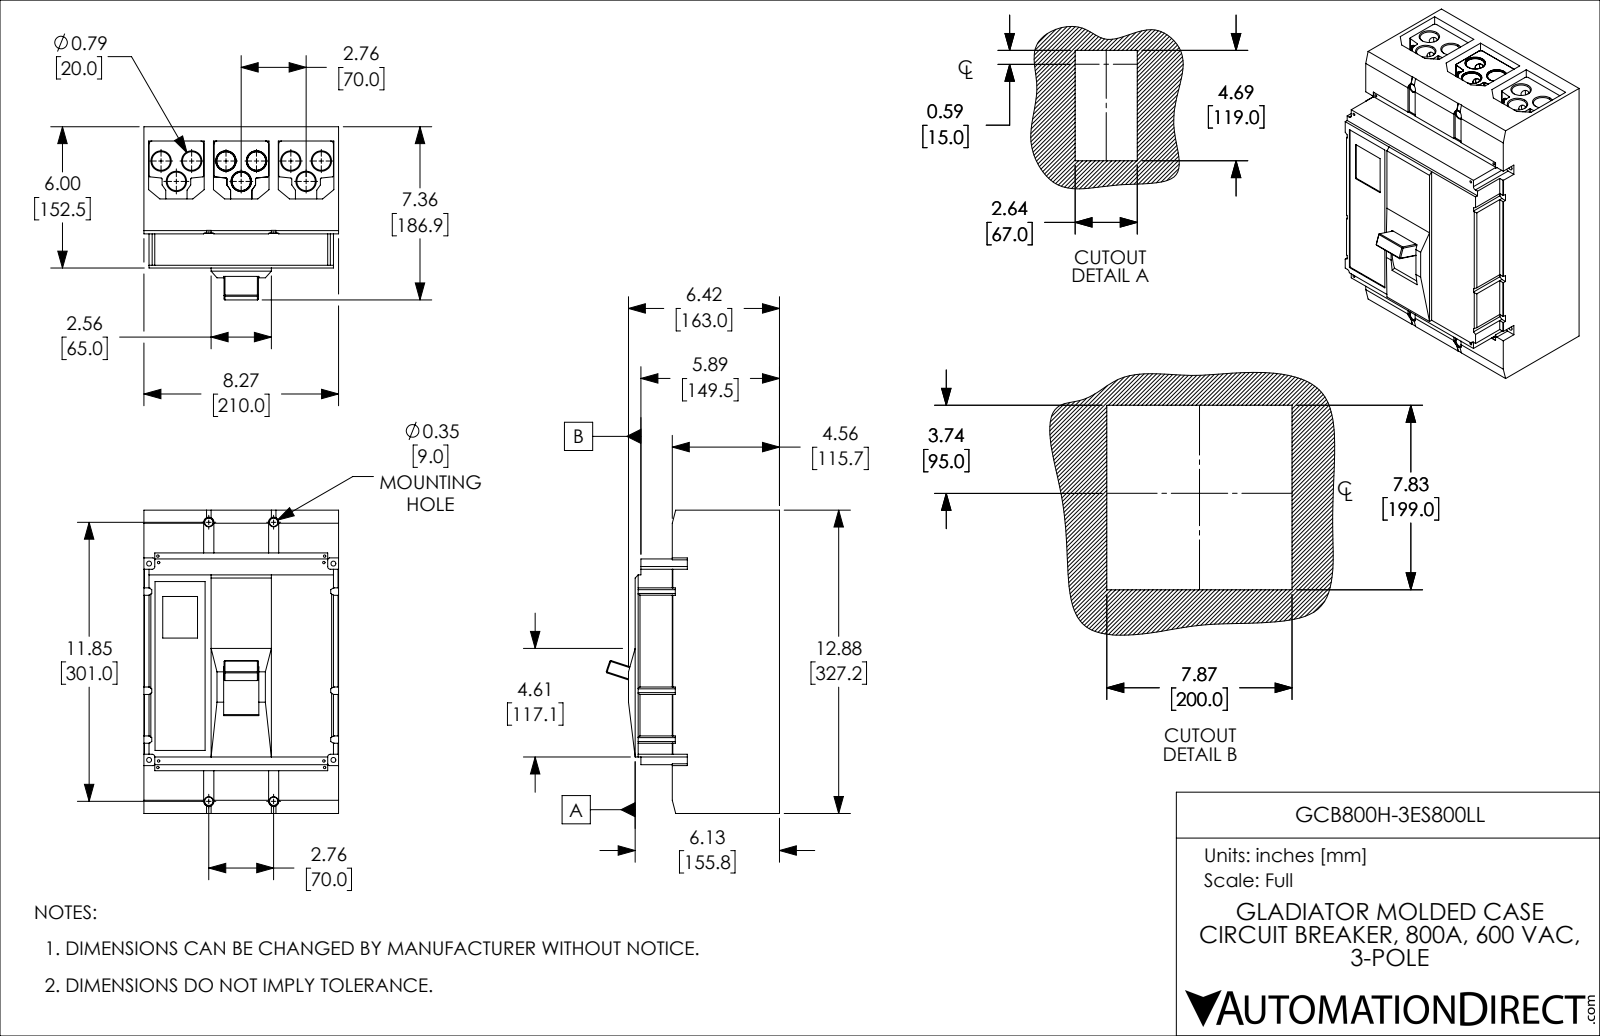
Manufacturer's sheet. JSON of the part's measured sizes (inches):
{"part_name": "GCB800H-3ES800LL", "step_written_by": "SolidWorks 2021 (CONFIG_CONTROL_DESIGN)", "units": "inches", "bodies": {"solids": 9, "faces": 1758, "planar": 450, "cylindrical": 778, "other": 530}, "overall_size": [12.882, 8.268, 7.358], "volume_in3": 540.2, "surface_area_in2": 832.4, "round_holes": [[0.472, 18], [0.268, 12], [0.566, 10], [0.787, 9], [0.102, 8], [0.566, 8], [0.209, 4], [0.354, 4]], "partial_cylinders_radius": [[0.039, 18], [0.354, 12], [0.118, 6], [0.079, 4], [0.114, 4], [0.217, 4], [3.227, 1], [3.885, 1]], "face_to_face_distances": [8.268, 0.61, 2.756, 1.969, 10.913, 0.02, 6.004, 5.394, 2.362, 2.343], "hole_center_spacings": [11.512, 11.181, 2.741, 2.741, 2.756, 12.452, 0.533, 5.481]}
